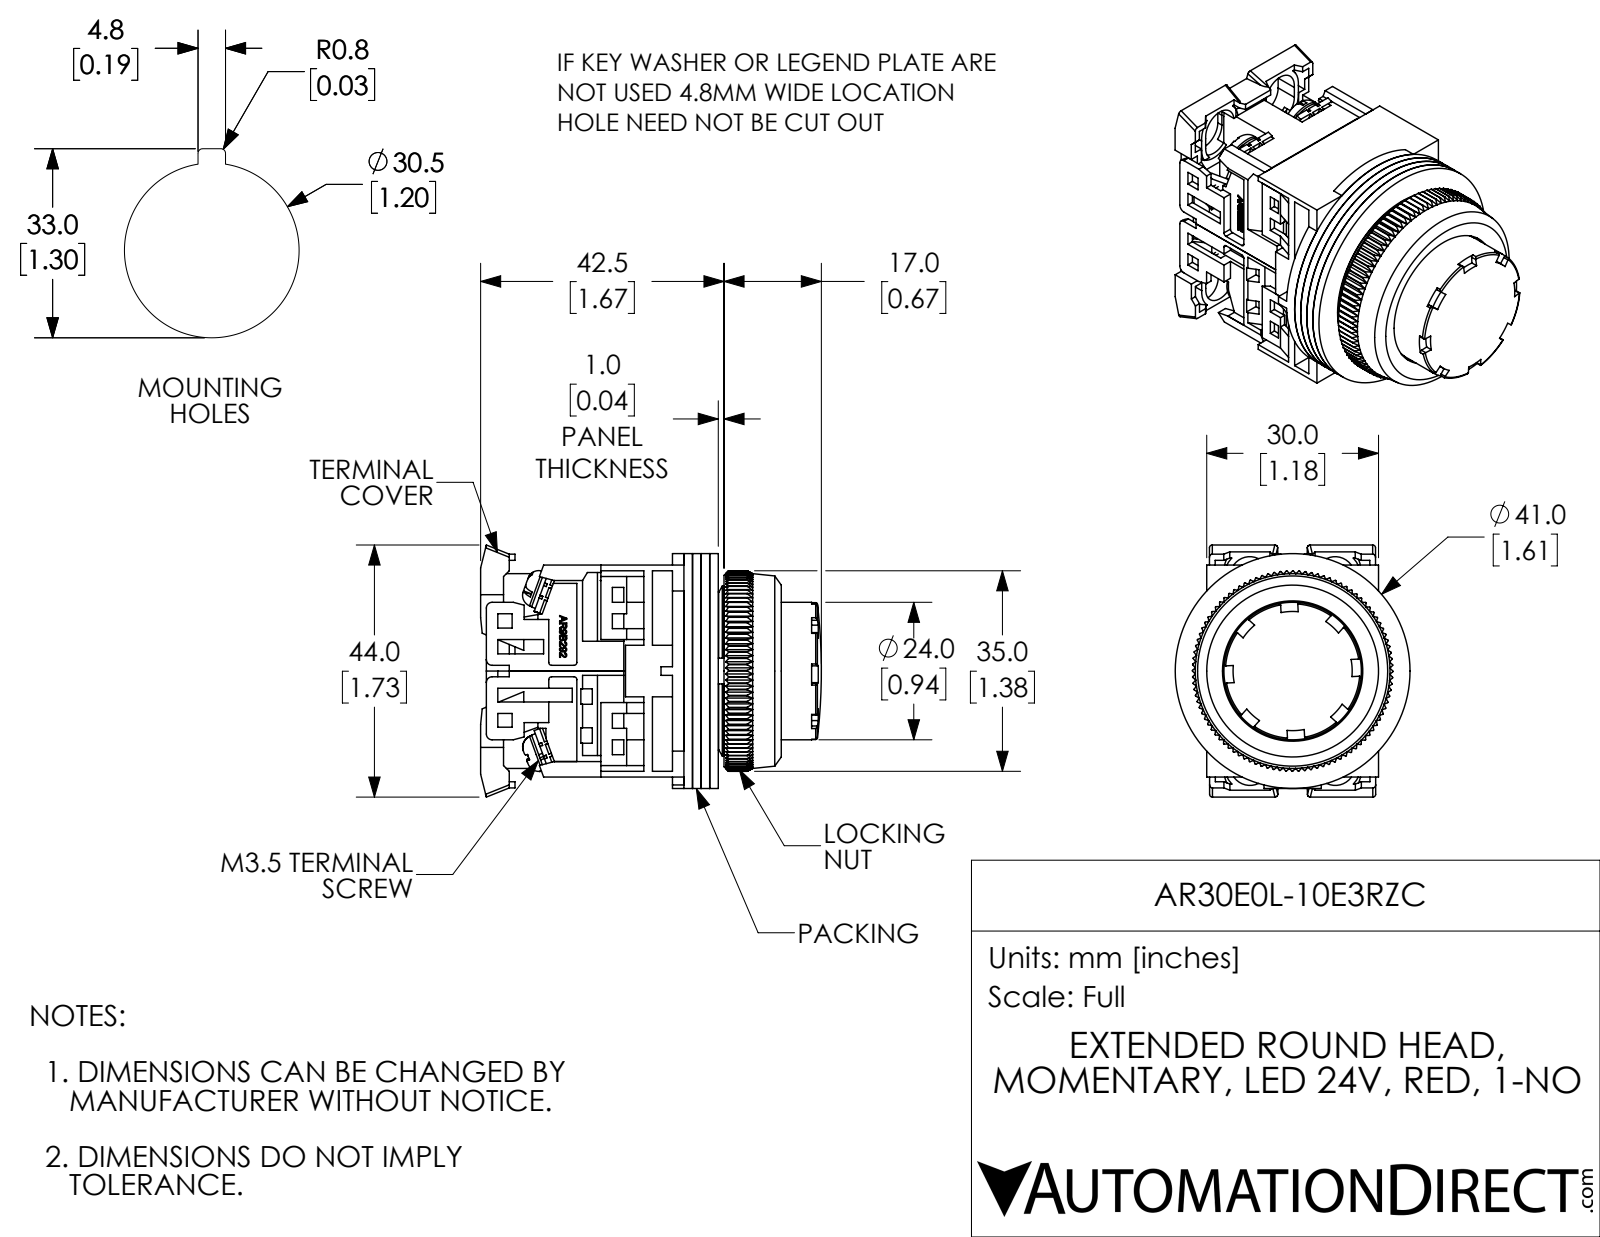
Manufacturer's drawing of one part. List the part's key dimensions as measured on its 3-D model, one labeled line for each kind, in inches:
Part name (STEP PRODUCT): AR30E0L-10E3RZC
STEP written by: SolidWorks 2017 (AUTOMOTIVE_DESIGN)
Units: inches
Bodies: 25 solids, 2022 faces (1378 planar, 323 cylindrical, 321 other)
Overall size (bounding box): 2.343 × 1.732 × 1.614
Volume: 2.119 in³ · Surface area: 59.85 in²
Round holes (diameter × count): ⌀0.138 ×8, ⌀0.142 ×4, ⌀0.118 ×1, ⌀0.472 ×1, ⌀0.709 ×1, ⌀0.728 ×1, ⌀0.787 ×1, ⌀0.945 ×1, ⌀0.965 ×1, ⌀1.122 ×1, ⌀1.252 ×1
Round bosses / shafts (diameter × count): ⌀0.26 ×4, ⌀0.138 ×4, ⌀1.614 ×1, ⌀1.181 ×1, ⌀0.866 ×1, ⌀0.776 ×1, ⌀0.551 ×1
Partial cylindrical surfaces — rounded edges, fillets, slot ends (radius × count): R0.012 ×16, R0.059 ×16, R0.02 ×12, R0.039 ×4, R0.138 ×4, R0.177 ×4, R0.118 ×2, R0.398 ×1
Main face-to-face distances: 0.059, 0.118, 0.039, 0.177, 0.811, 1.417, 0.634, 0.079, 1.358, 0.689
Hole centre spacings: 0.579, 0.61
